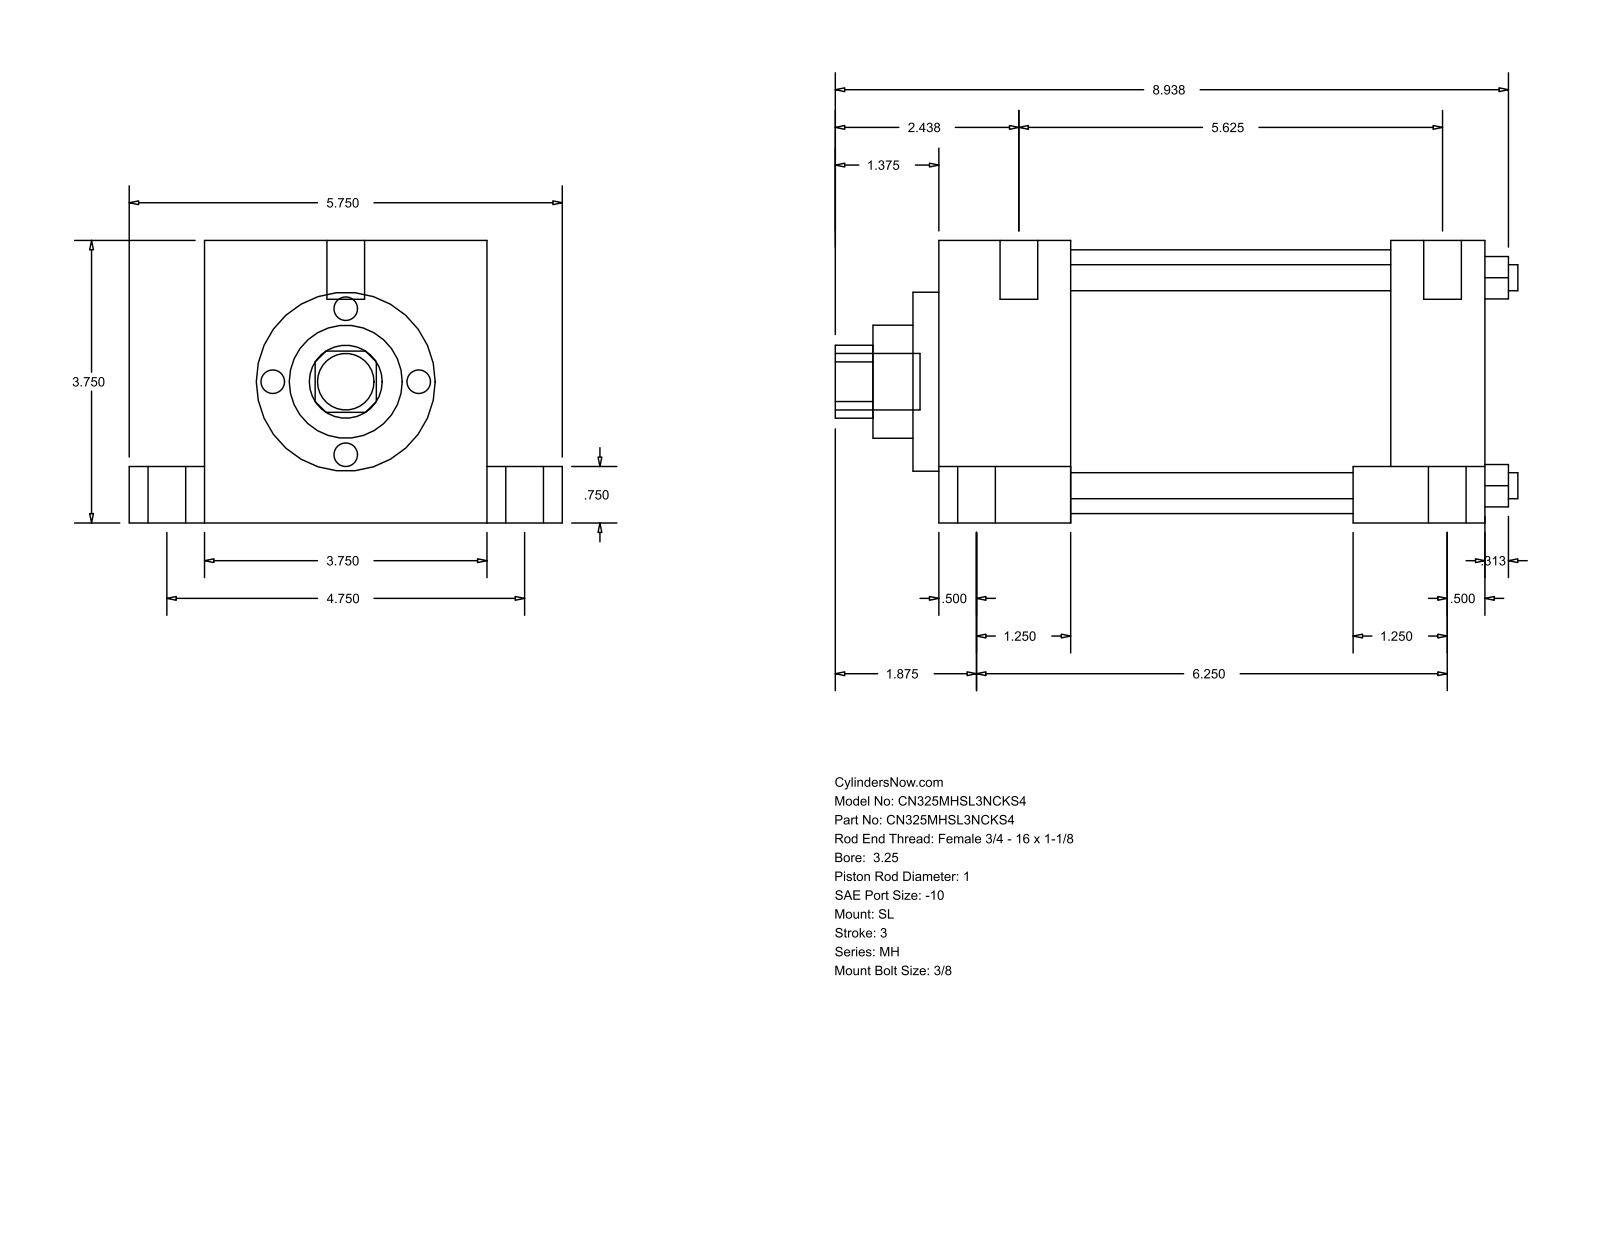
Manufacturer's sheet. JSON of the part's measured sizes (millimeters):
{"part_name": "MH_SL__0325_1", "step_written_by": "GSSL Pune (CONFIG_CONTROL_DESIGN)", "units": "millimeters", "bodies": {"solids": 0, "faces": 110, "planar": 77, "cylindrical": 33, "other": 0}, "overall_size": [230.19, 146.05, 95.25], "round_holes": [[8.76, 4], [25.4, 1], [38.1, 1], [60.33, 1], [88.9, 1]], "round_bosses_or_shafts": [[12.7, 6], [19.05, 5], [5.56, 4]], "partial_cylinders_radius": [[12.29, 1]], "face_to_face_distances": [95.24, 184.15, 44.46, 139.69, 25.41, 120.65, 19.05, 76.19, 152.4, 107.94], "hole_center_spacings": [49.57, 70.1, 99.14]}
